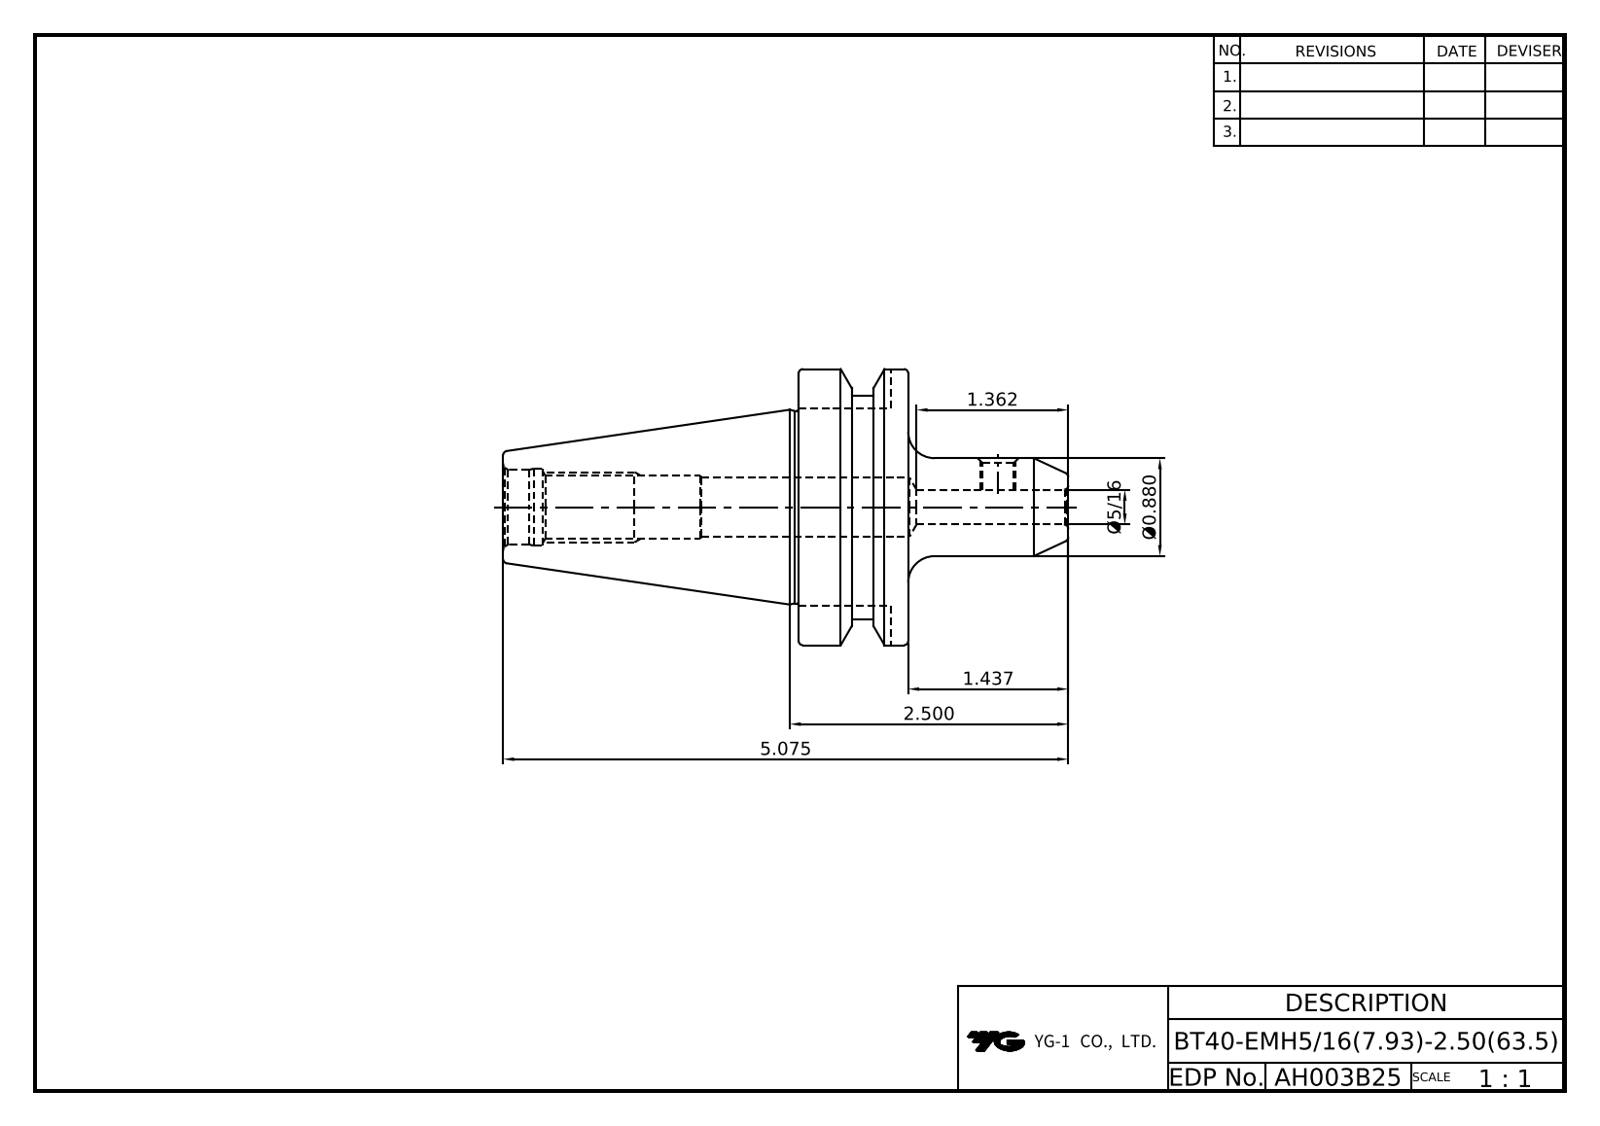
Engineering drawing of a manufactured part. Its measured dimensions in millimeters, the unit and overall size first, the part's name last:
Units: millimetres
Overall size (bounding box): 128.9 × 63 × 63
Round holes (diameter × count): ⌀6.78 ×1, ⌀7.94 ×1, ⌀13.5 ×1, ⌀13.84 ×1, ⌀17 ×1, ⌀17.6 ×1
Round bosses / shafts (diameter × count): ⌀63 ×1, ⌀52.6 ×1, ⌀44 ×1, ⌀22.35 ×1
Partial cylindrical surfaces — rounded edges, fillets, slot ends (radius × count): R8.05 ×1
Main face-to-face distances: 25, 45.2, 16.1, 67.4, 92.4, 84.5, 17.1, 7.9, 79.5, 12.1
Volume: 131 620 mm³ · Surface area: 25 705 mm²
Bodies: 1 solid, 49 faces (15 planar, 15 cylindrical, 19 other)
Part name (STEP PRODUCT): LO-BT40-EMH7.9375-63.5
STEP written by: Autodesk Inventor 2022 (AUTOMOTIVE_DESIGN)
